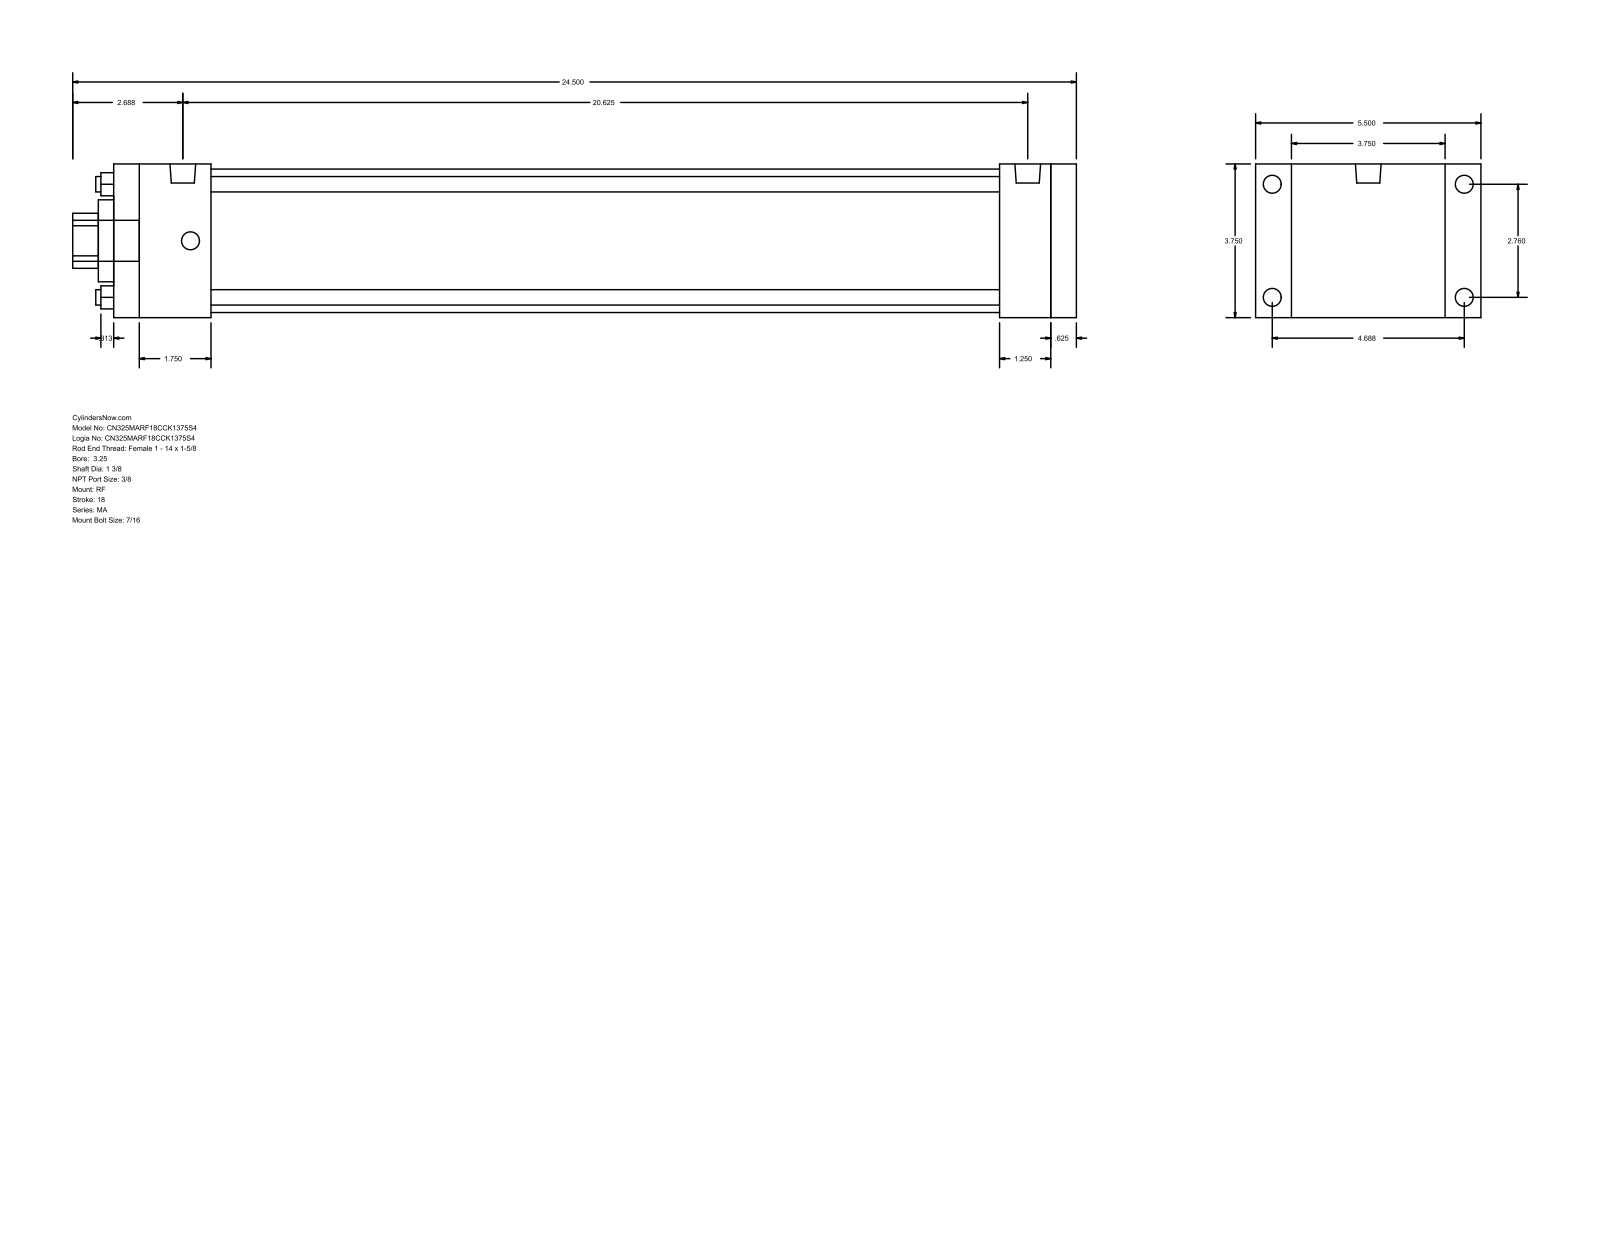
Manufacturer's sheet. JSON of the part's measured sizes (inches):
{"part_name": "MA_RF__0325_1.375", "step_written_by": "GSSL Pune (CONFIG_CONTROL_DESIGN)", "units": "inches", "bodies": {"solids": 0, "faces": 92, "planar": 64, "cylindrical": 28, "other": 0}, "overall_size": [24.5, 5.5, 3.75], "round_holes": [[0.375, 4], [1.375, 1], [2, 1], [3.5, 1]], "round_bosses_or_shafts": [[0.437, 8], [0.627, 2], [1, 1]], "partial_cylinders_radius": [[0.672, 1]], "face_to_face_distances": [3.75, 23.5, 0.625, 22.875, 0.875, 4.625, 21.625, 1.25, 1.875, 2.375], "hole_center_spacings": [1.952, 2.76, 3.903]}
